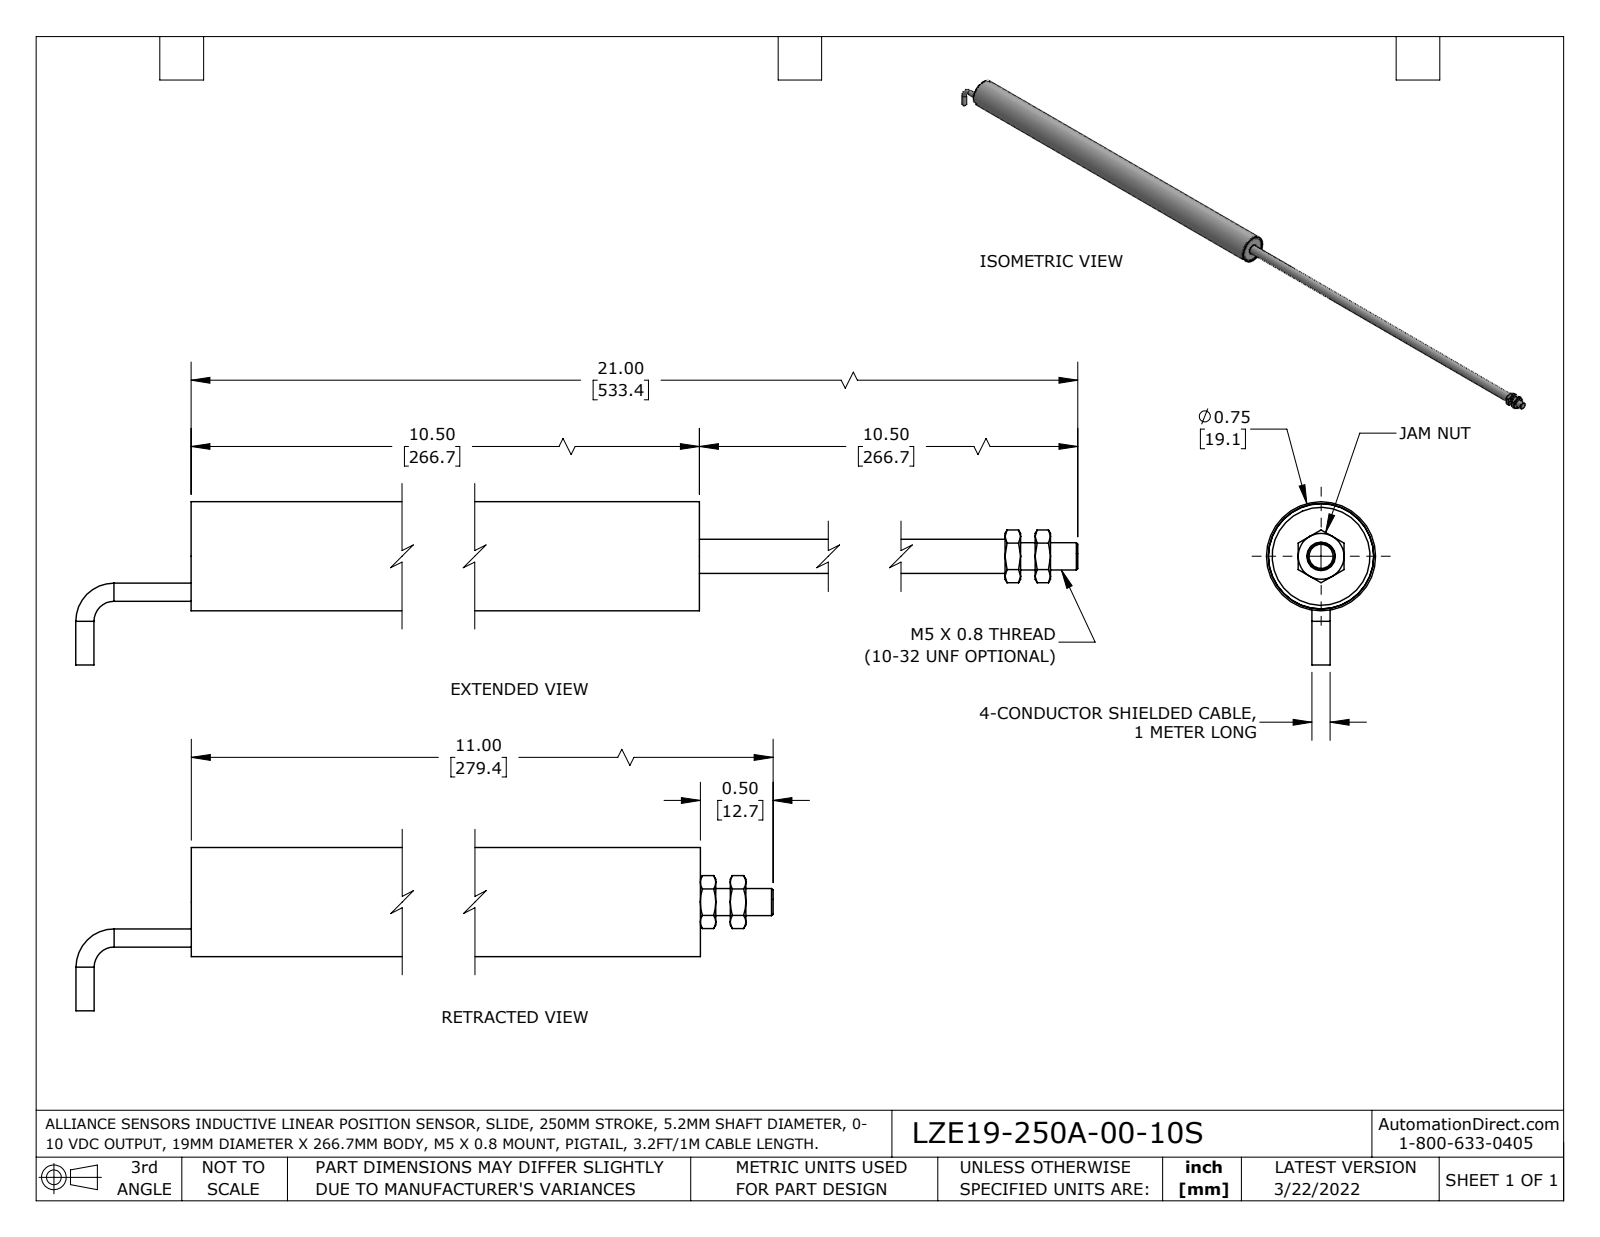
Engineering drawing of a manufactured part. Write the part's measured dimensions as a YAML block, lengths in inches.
part_name: "3120-0006-06_-10-0Y; 5300-0002; 3100-0076_B18.2.4.5M - Hex jam nut, M5 x 0.8 --D-N; 3120-0008-06_-10 (+6 more)"
step_written_by: "SolidWorks 2021 (AUTOMOTIVE_DESIGN)"
units: inches
bodies: {solids: 10, faces: 137, planar: 42, cylindrical: 44, other: 51}
overall_size: [21.793, 1.121, 0.75]
volume: 1.569
surface_area: 88.58
round_holes:
  - {diameter: 0.165, count: 1}
  - {diameter: 0.188, count: 1}
  - {diameter: 0.197, count: 1}
  - {diameter: 0.234, count: 1}
  - {diameter: 0.281, count: 1}
  - {diameter: 0.68, count: 1}
  - {diameter: 0.725, count: 1}
round_bosses_or_shafts:
  - {diameter: 0.125, count: 2}
  - {diameter: 0.75, count: 1}
  - {diameter: 0.723, count: 1}
  - {diameter: 0.278, count: 1}
  - {diameter: 0.187, count: 1}
partial_cylinders:
  - {radius: 0.052, count: 1}
face_to_face_distances: [0.06, 10.42, 0.08, 10.36, 10.48, 0.315, 0.206, 0.106, 0.374, 10.5]
